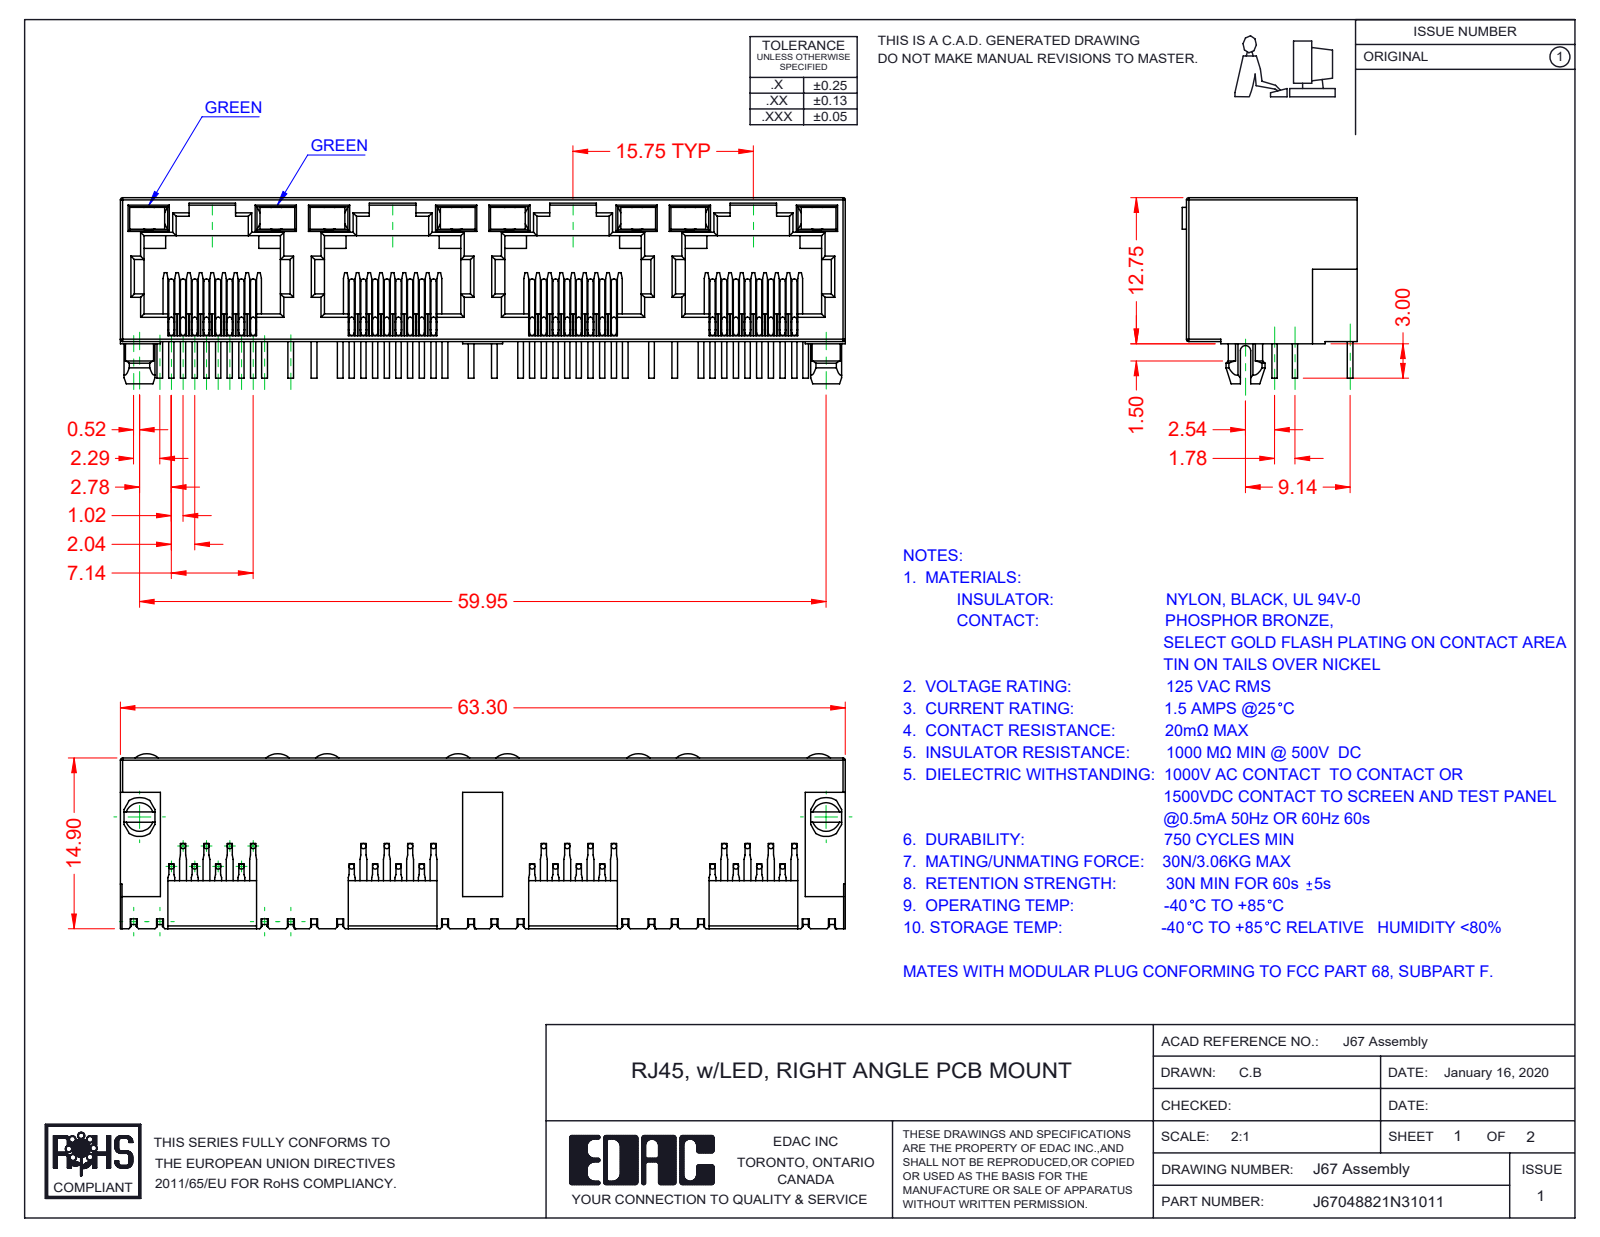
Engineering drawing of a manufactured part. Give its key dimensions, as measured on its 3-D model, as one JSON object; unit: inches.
{"part_name": "J67048822N33011; 67 Contacts; 67 LED LH_3-Green; 67 Insulator (+1 more)", "step_written_by": "SolidWorks 2016 (CONFIG_CONTROL_DESIGN)", "units": "inches", "bodies": {"solids": 41, "faces": 2465, "planar": 1781, "cylindrical": 476, "other": 208}, "overall_size": [2.492, 0.64, 0.602], "volume_in3": 0.315, "surface_area_in2": 17.94, "round_bosses_or_shafts": [[0.018, 96]], "partial_cylinders_radius": [[0.008, 66], [0.012, 29], [0.018, 9], [0.061, 8], [0.059, 2], [0.067, 2], [0.014, 1], [0.039, 1]], "face_to_face_distances": [0.02, 0.494, 0.074, 0.035, 0.394, 0.62, 0.039, 0.055, 0.433, 0.468]}
